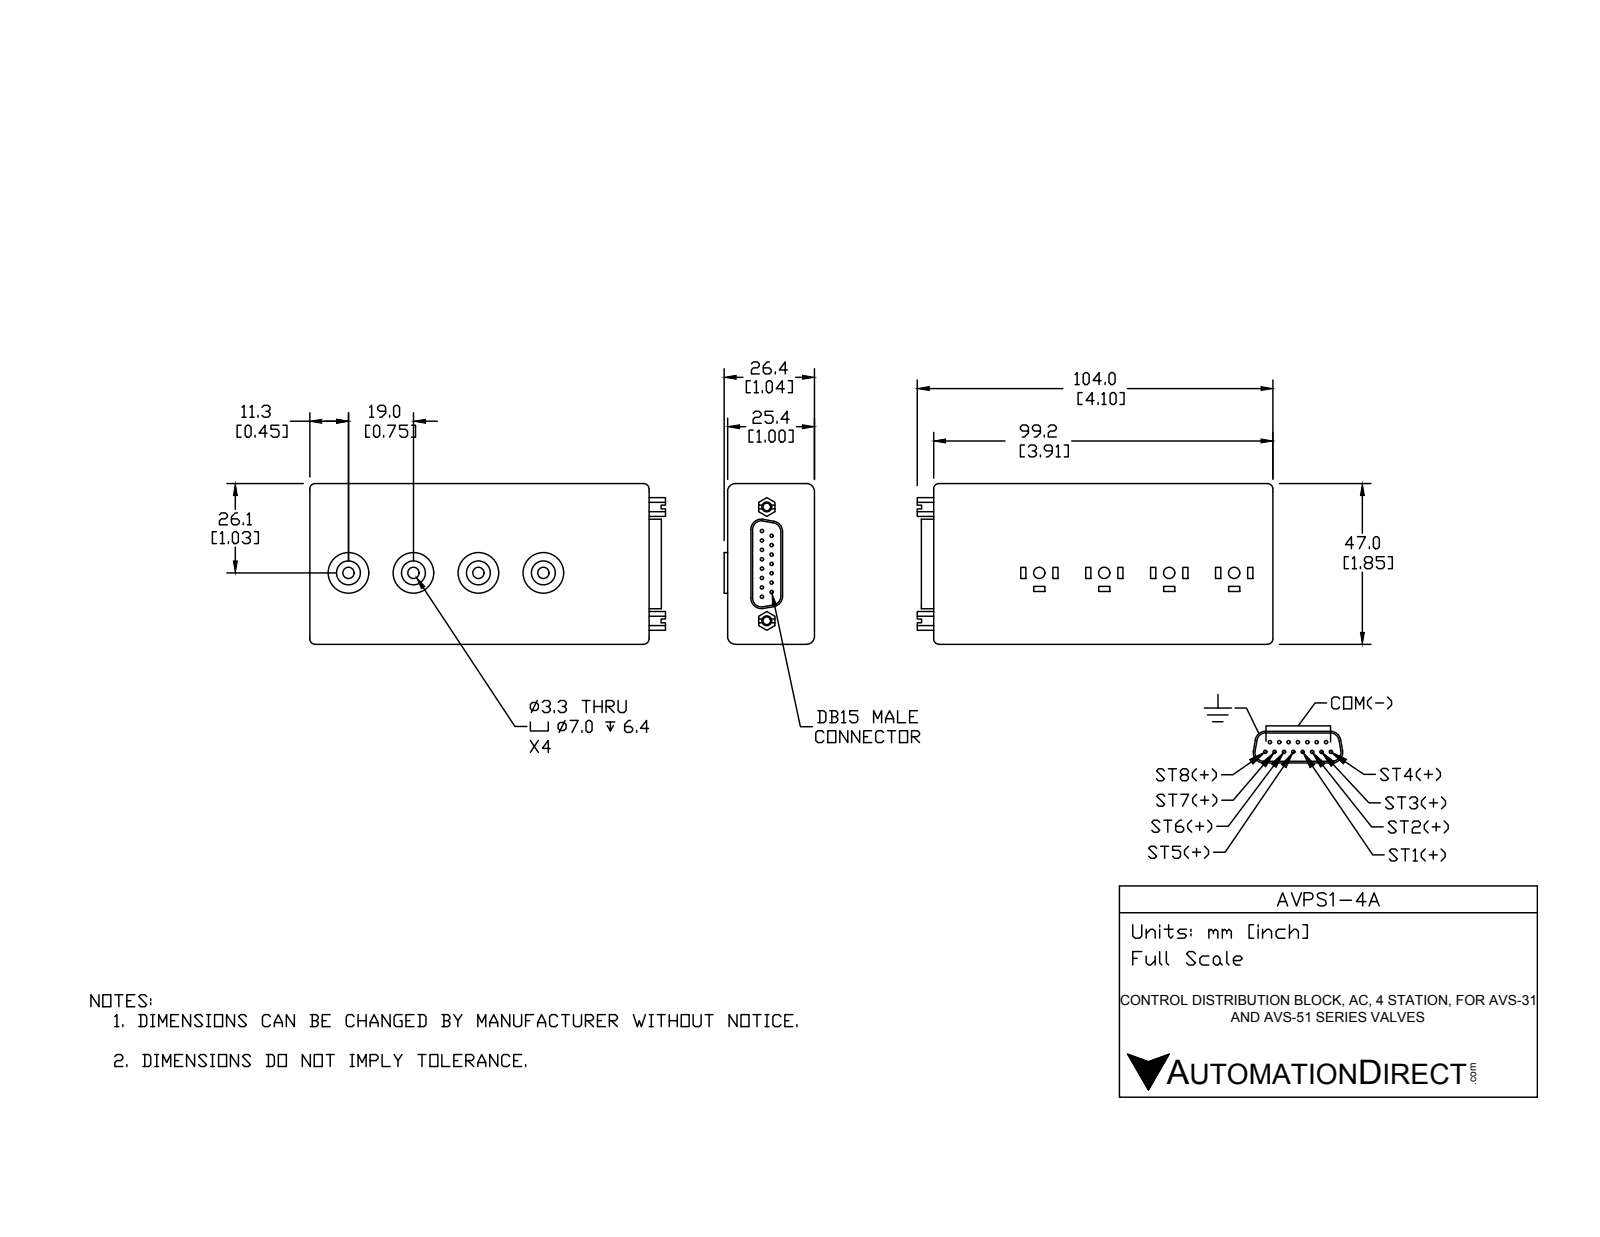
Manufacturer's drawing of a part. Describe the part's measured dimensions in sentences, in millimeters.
The part is named "AVPS1-4A". Its 3-D file was written by "SolidWorks 2016 (AUTOMOTIVE_DESIGN)". It is 1 solid with 219 faces: 127 planar, 80 cylindrical and 12 other. Overall it measures 104 by 47 by 26.4 millimeters. Its volume is 116 000 cubic millimeters and its surface area 19 490 square millimeters. Round holes: 4 of diameter 3.3, 4 of diameter 7, 2 of diameter 2.3. Round bosses or shafts: 15 of diameter 1, 4 of diameter 11.9. Partial cylindrical surfaces (rounded edges, fillets, slot ends): 6 of radius 1.6, 4 of radius 2.3, 4 of radius 2.6, 4 of radius 3.1, 2 of radius 1.6. The main face-to-face distances are 25.4, 47, 99.2, 1, 26.4, 1.5, 19, 3.1, 96.1, 6.4. The hole center spacings are 19, 38, 33.3, 57.
